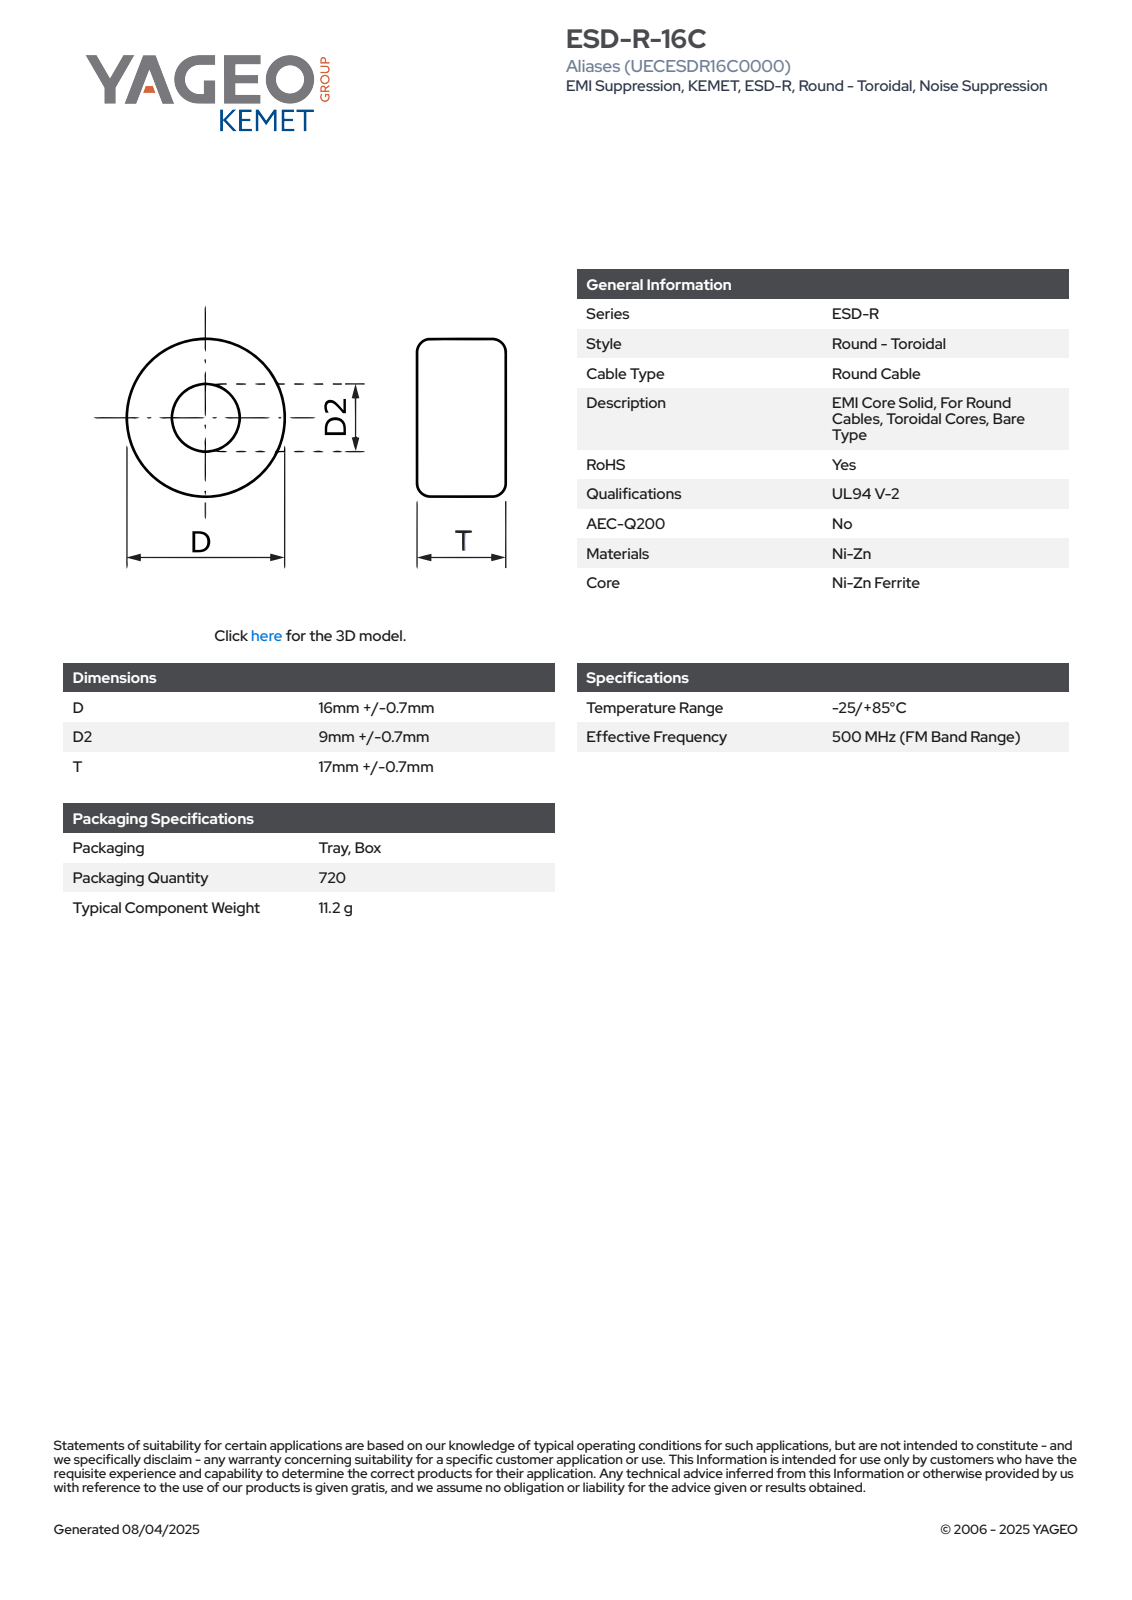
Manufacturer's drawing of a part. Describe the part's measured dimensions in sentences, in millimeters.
The part is named "EC_KBC_D16.7D29T17.7". Its 3-D file was written by "SolidWorks 2021 (AUTOMOTIVE_DESIGN)". It is 1 solid with 66 faces: 24 planar, 7 cylindrical and 35 other. Overall it measures 17.7 by 16.71 by 16.7 millimeters. Its volume is 2 745 cubic millimeters and its surface area 1 719 square millimeters. Round holes: 1 of diameter 9. Round bosses or shafts: 1 of diameter 16.7. Partial cylindrical surfaces (rounded edges, fillets, slot ends): 1 of radius 8.36. The main face-to-face distances are 17.7, 8, 9.7, 1.7, 0.32, 8.32, 9.38, 1.38, 1.06, 9.06.
